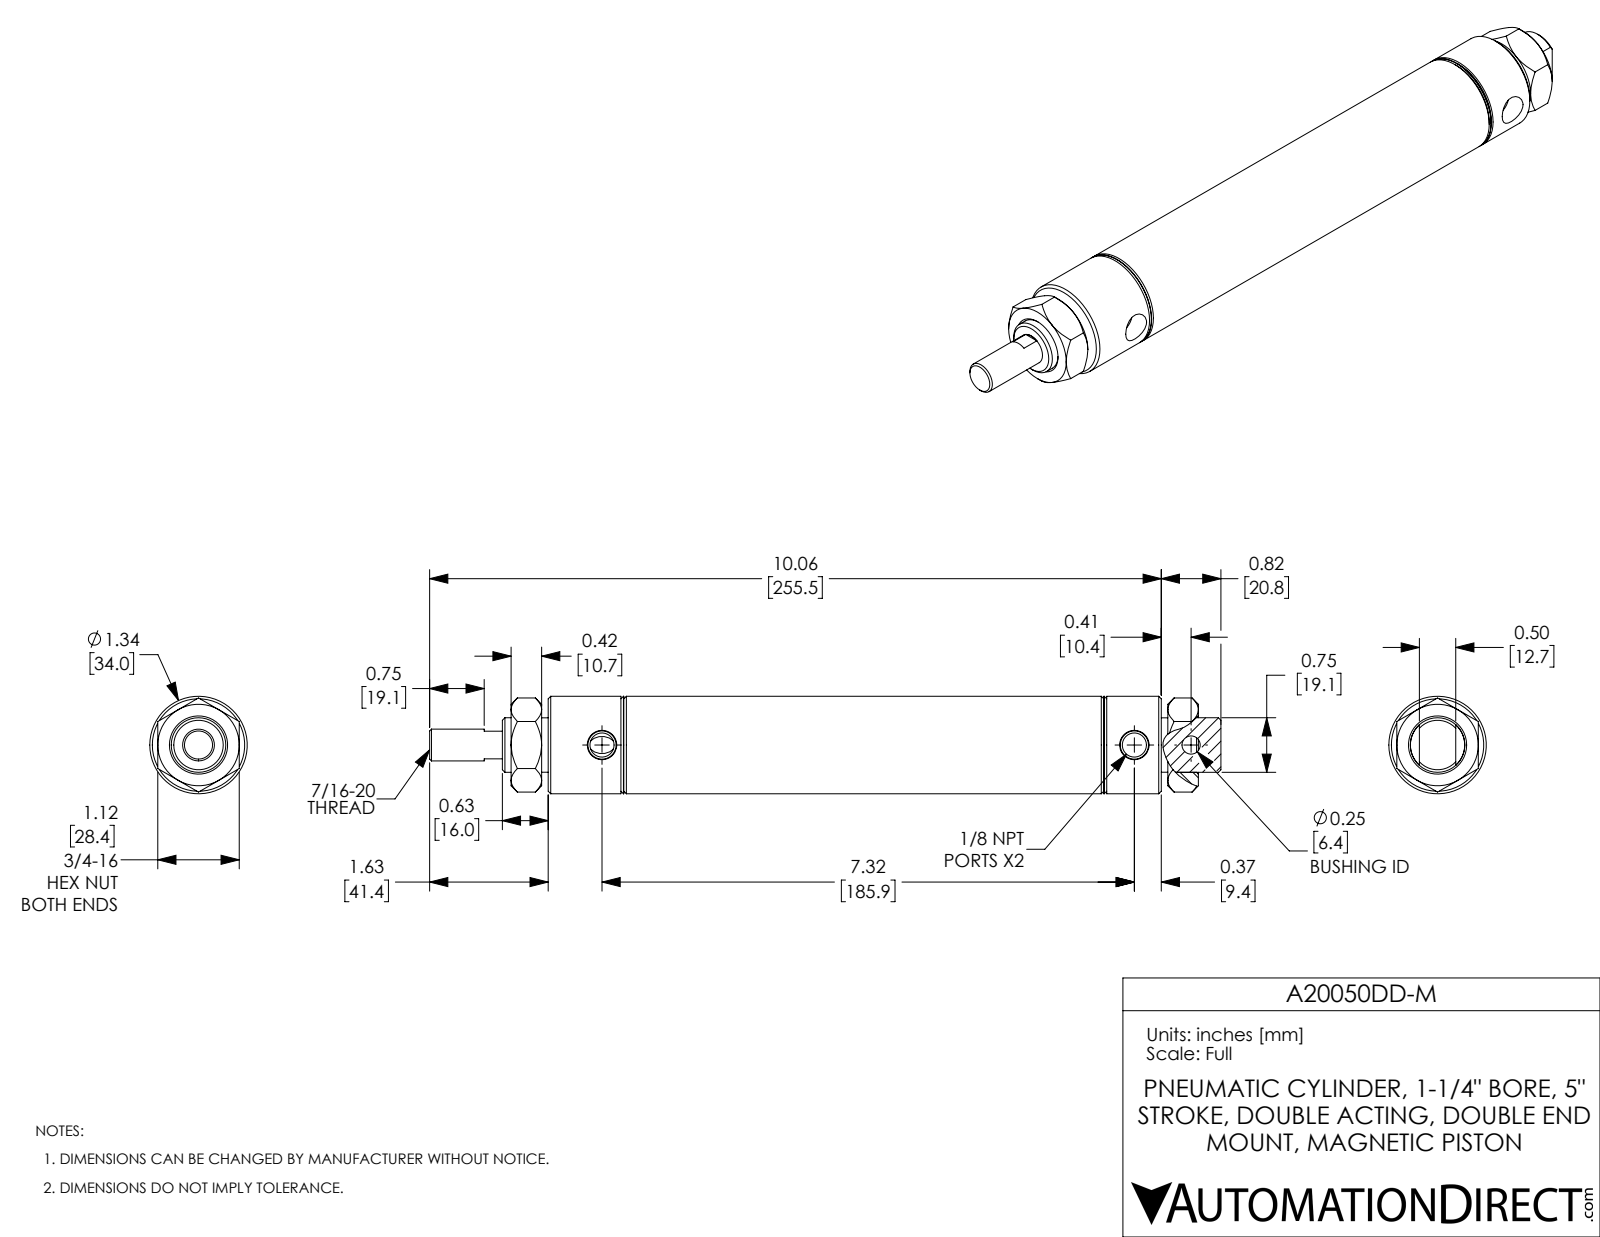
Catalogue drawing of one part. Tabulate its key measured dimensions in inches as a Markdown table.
| quantity | value |
| --- | --- |
| part name | A20050DD-M; A20050DD-M_Mounting Nut_D-3556; A20050DD-M-Rod; A20050DD-M-MainBody |
| STEP written by | SolidWorks 2017 (AUTOMOTIVE_DESIGN) |
| units | inches |
| bodies | 4 solids, 138 faces (44 planar, 36 cylindrical, 58 other) |
| overall size | 10.88 × 1.34 × 1.34 |
| volume | 7.604 in³ |
| surface area | 92.9 in² |
| round holes (diameter × count) | 0.332 × 2, 0.251 × 1, 0.437 × 1, 0.75 × 1, 1.25 × 1 |
| round bosses / shafts (diameter × count) | 1.34 × 1, 0.747 × 1 |
| main face-to-face distances | 1.465, 6.965, 0.5, 1.12, 5.5, 5, 0.31, 0.42, 9.03, 1.965 |
| hole center spacings | 0.78, 7.32, 8.1 |
